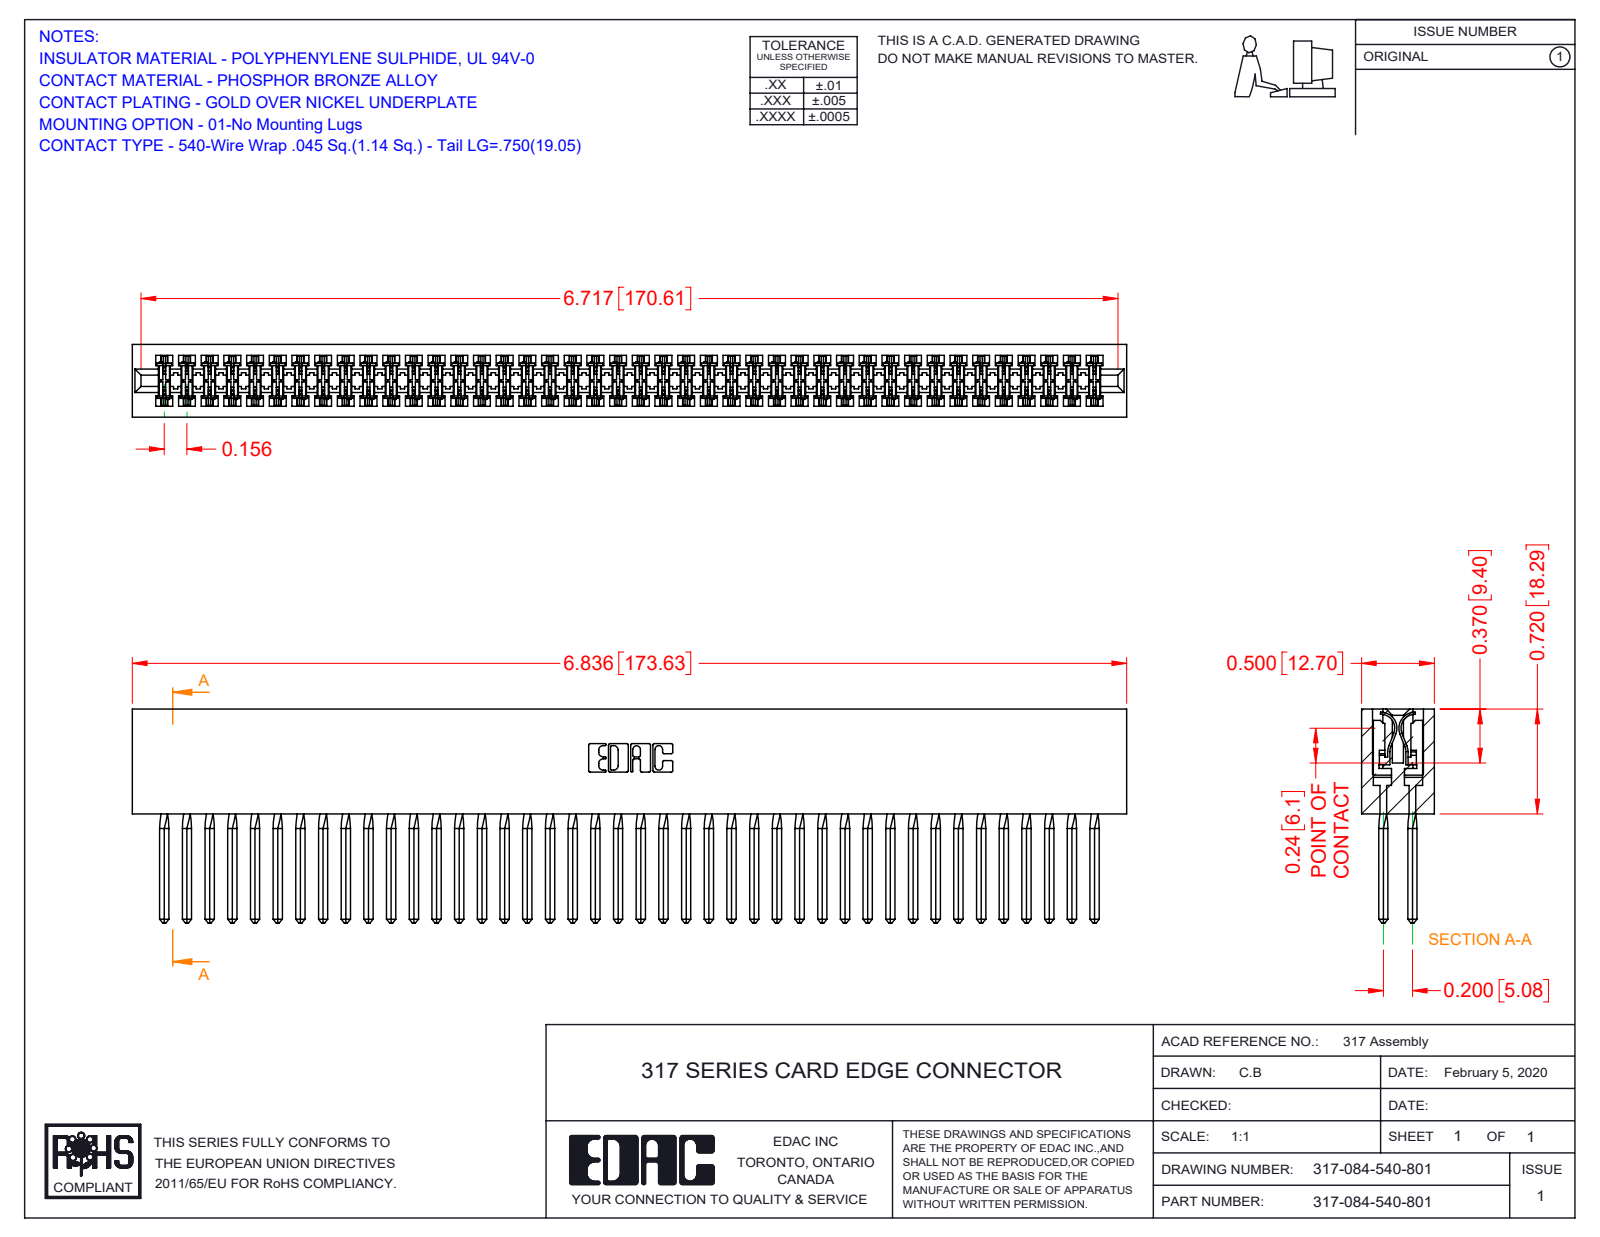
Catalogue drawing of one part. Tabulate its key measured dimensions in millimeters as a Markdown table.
| quantity | value |
| --- | --- |
| part name | 317 Part_Lugless; 317-084-540-801; 317-290-001_540 |
| STEP written by | SolidWorks 2016 (CONFIG_CONTROL_DESIGN) |
| units | millimeters |
| bodies | 85 solids, 7566 faces (6182 planar, 1048 cylindrical, 336 other) |
| overall size | 173.6 × 37.3 × 12.7 |
| volume | 30 940 mm³ |
| surface area | 46 380 mm² |
| partial cylindrical surfaces (radius × count) | 0.4 × 168, 0.3 × 22, 0.2 × 6, 0.8 × 6, 0.7 × 3, 2.4 × 2, 2.5 × 2, 2.8 × 2 |
| main face-to-face distances | 1.9, 12.7, 10.8, 8.9, 5, 2.4, 5.1, 2.9, 3.3, 1.2 |
